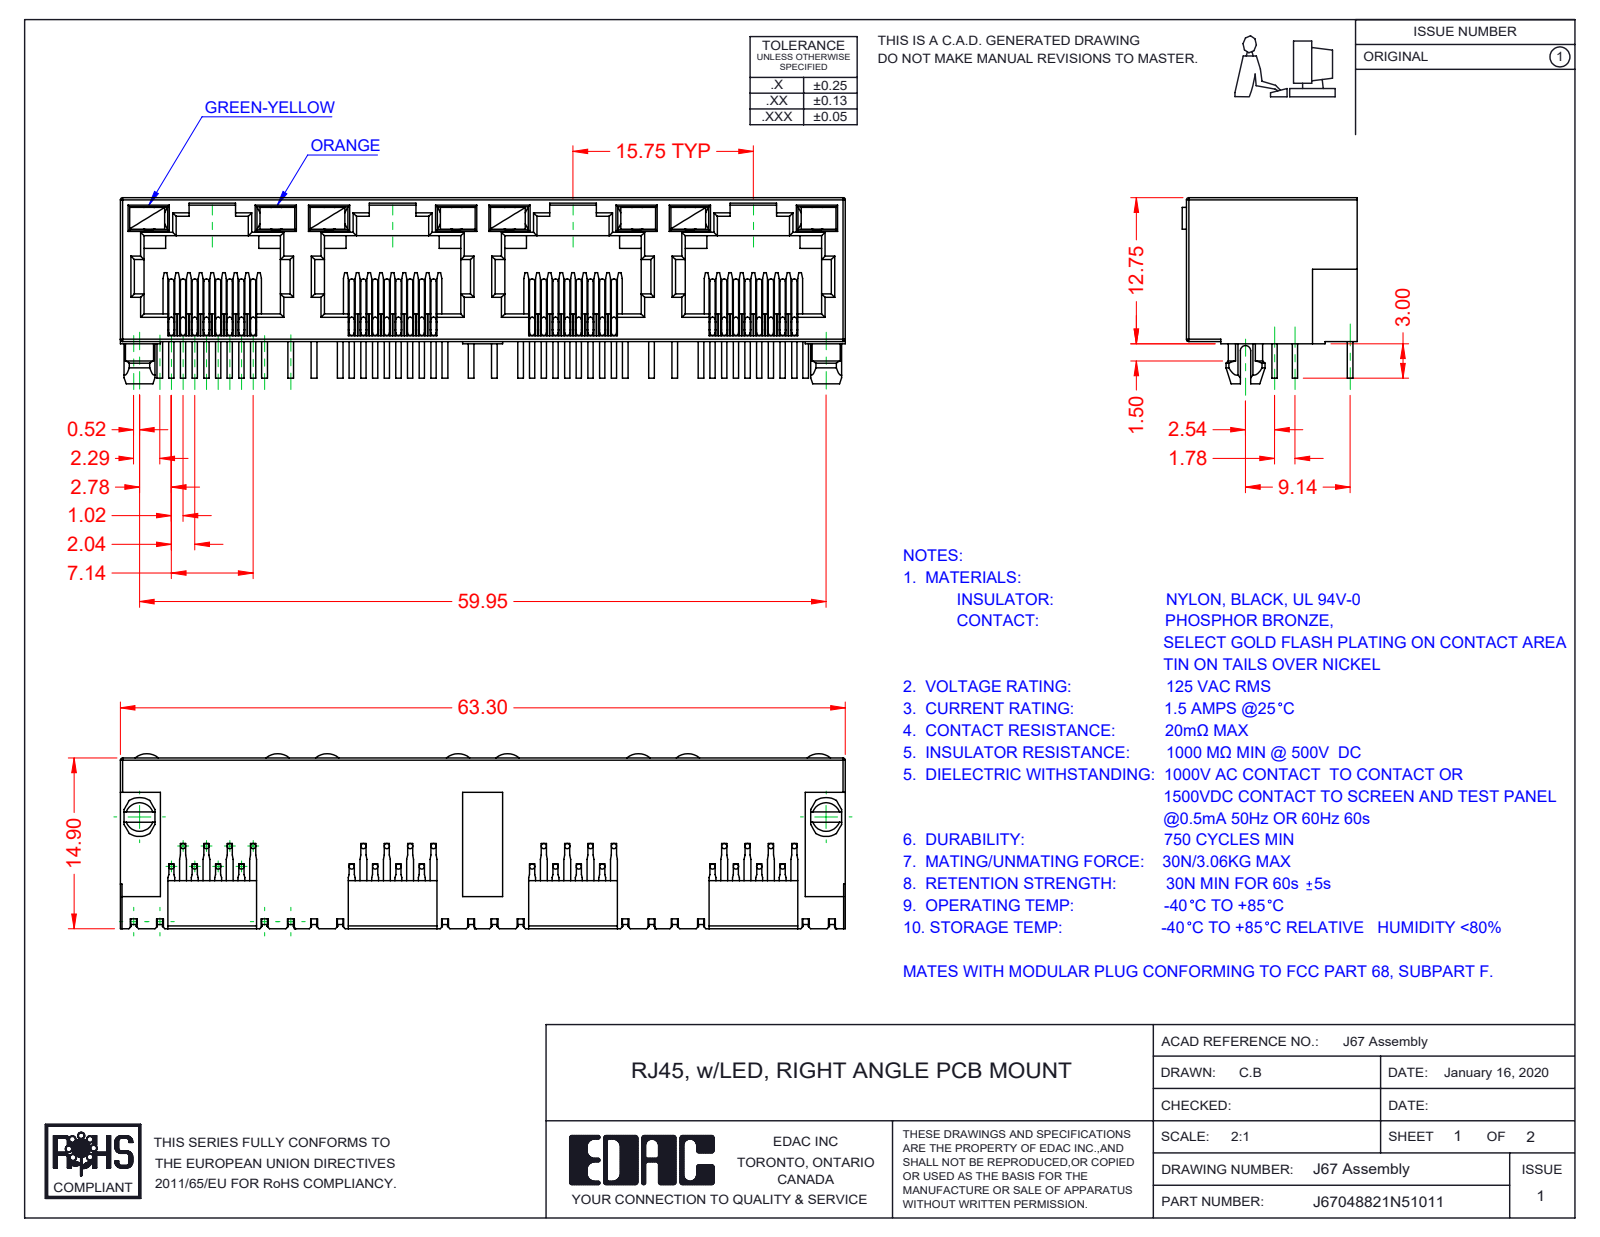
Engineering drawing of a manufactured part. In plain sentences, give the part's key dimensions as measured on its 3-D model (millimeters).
The part is named "67 Contacts; J67048822N54011; 67 LED RH_4-Orange; 67 LED LH_5-Green-Yellow (+1 more)". Its 3-D file was written by "SolidWorks 2016 (CONFIG_CONTROL_DESIGN)". It is 41 solids with 2473 faces: 1781 planar, 484 cylindrical and 208 other. Overall it measures 63.3 by 16.25 by 15.28 millimeters. Its volume is 5 159 cubic millimeters and its surface area 11 573 square millimeters. Round bosses or shafts: 96 of diameter 0.46. Partial cylindrical surfaces (rounded edges, fillets, slot ends): 66 of radius 0.2, 29 of radius 0.3, 9 of radius 0.45, 8 of radius 1.55, 2 of radius 1.5, 2 of radius 1.7, 1 of radius 0.35, 1 of radius 1. The main face-to-face distances are 0.5, 12.55, 1.89, 0.89, 10, 15.75, 1, 1.39, 11, 11.89.
